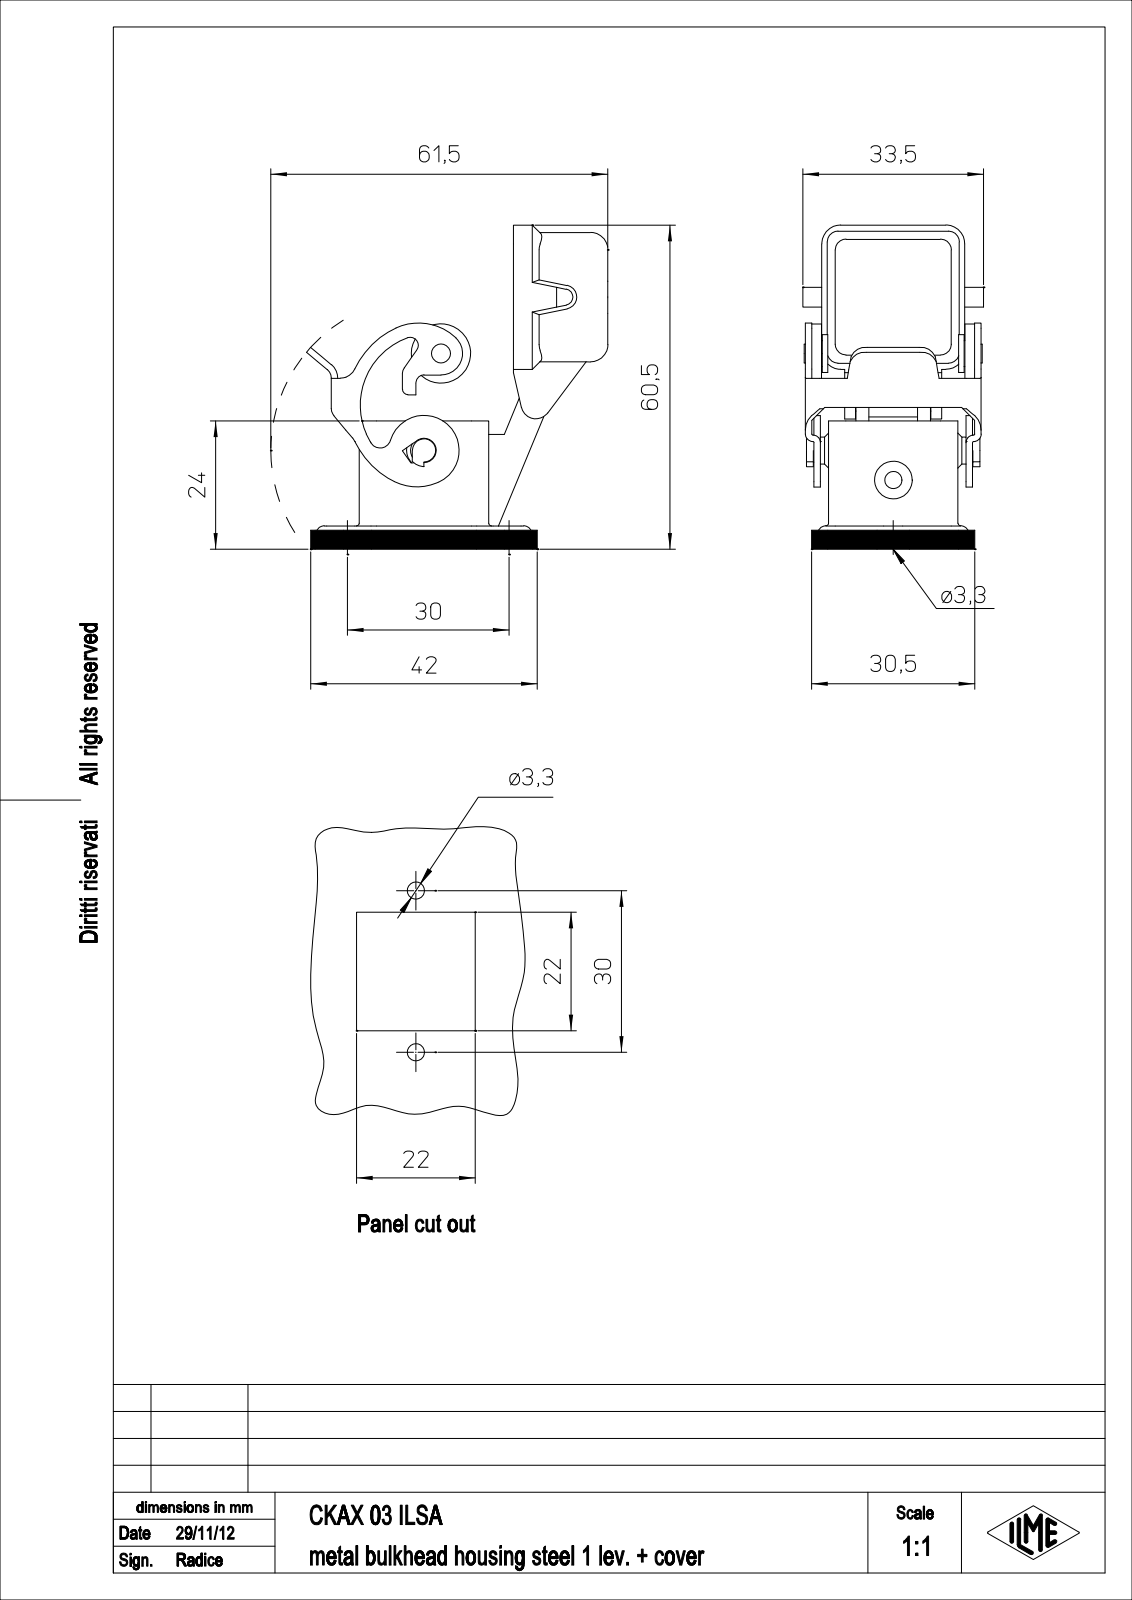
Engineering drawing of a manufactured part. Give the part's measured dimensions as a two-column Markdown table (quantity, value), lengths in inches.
| quantity | value |
| --- | --- |
| part name | CKAX_03_ILSA |
| STEP written by | Creo Elements/Direct Modeling 18.0B 02-Dec-2011 (C) Parametric Technology GmbH (AUTOMOTIVE_DESIGN) |
| units | inches |
| bodies | 1 solid, 380 faces (184 planar, 165 cylindrical, 31 other) |
| overall size | 2.368 × 2.213 × 1.319 |
| volume | 0.633 in³ |
| surface area | 21.19 in² |
| round holes (diameter × count) | 0.13 × 2, 0.126 × 1, 0.197 × 1, 0.276 × 1 |
| round bosses / shafts (diameter × count) | 0.433 × 1, 0.276 × 1, 0.197 × 1, 0.189 × 1, 0.169 × 1, 0.166 × 1, 0.138 × 1, 0.079 × 1 |
| partial cylindrical surfaces (radius × count) | 0.079 × 20, 0.008 × 19, 0.126 × 13, 0.059 × 9, 0.236 × 6, 0.118 × 5, 0.02 × 4, 0.055 × 4 |
| main face-to-face distances | 0.047, 0.945, 0.169, 0.898, 0.85, 0.106, 1.004, 0.154, 1.067, 0.063 |
| hole center spacings | 1.181 |
